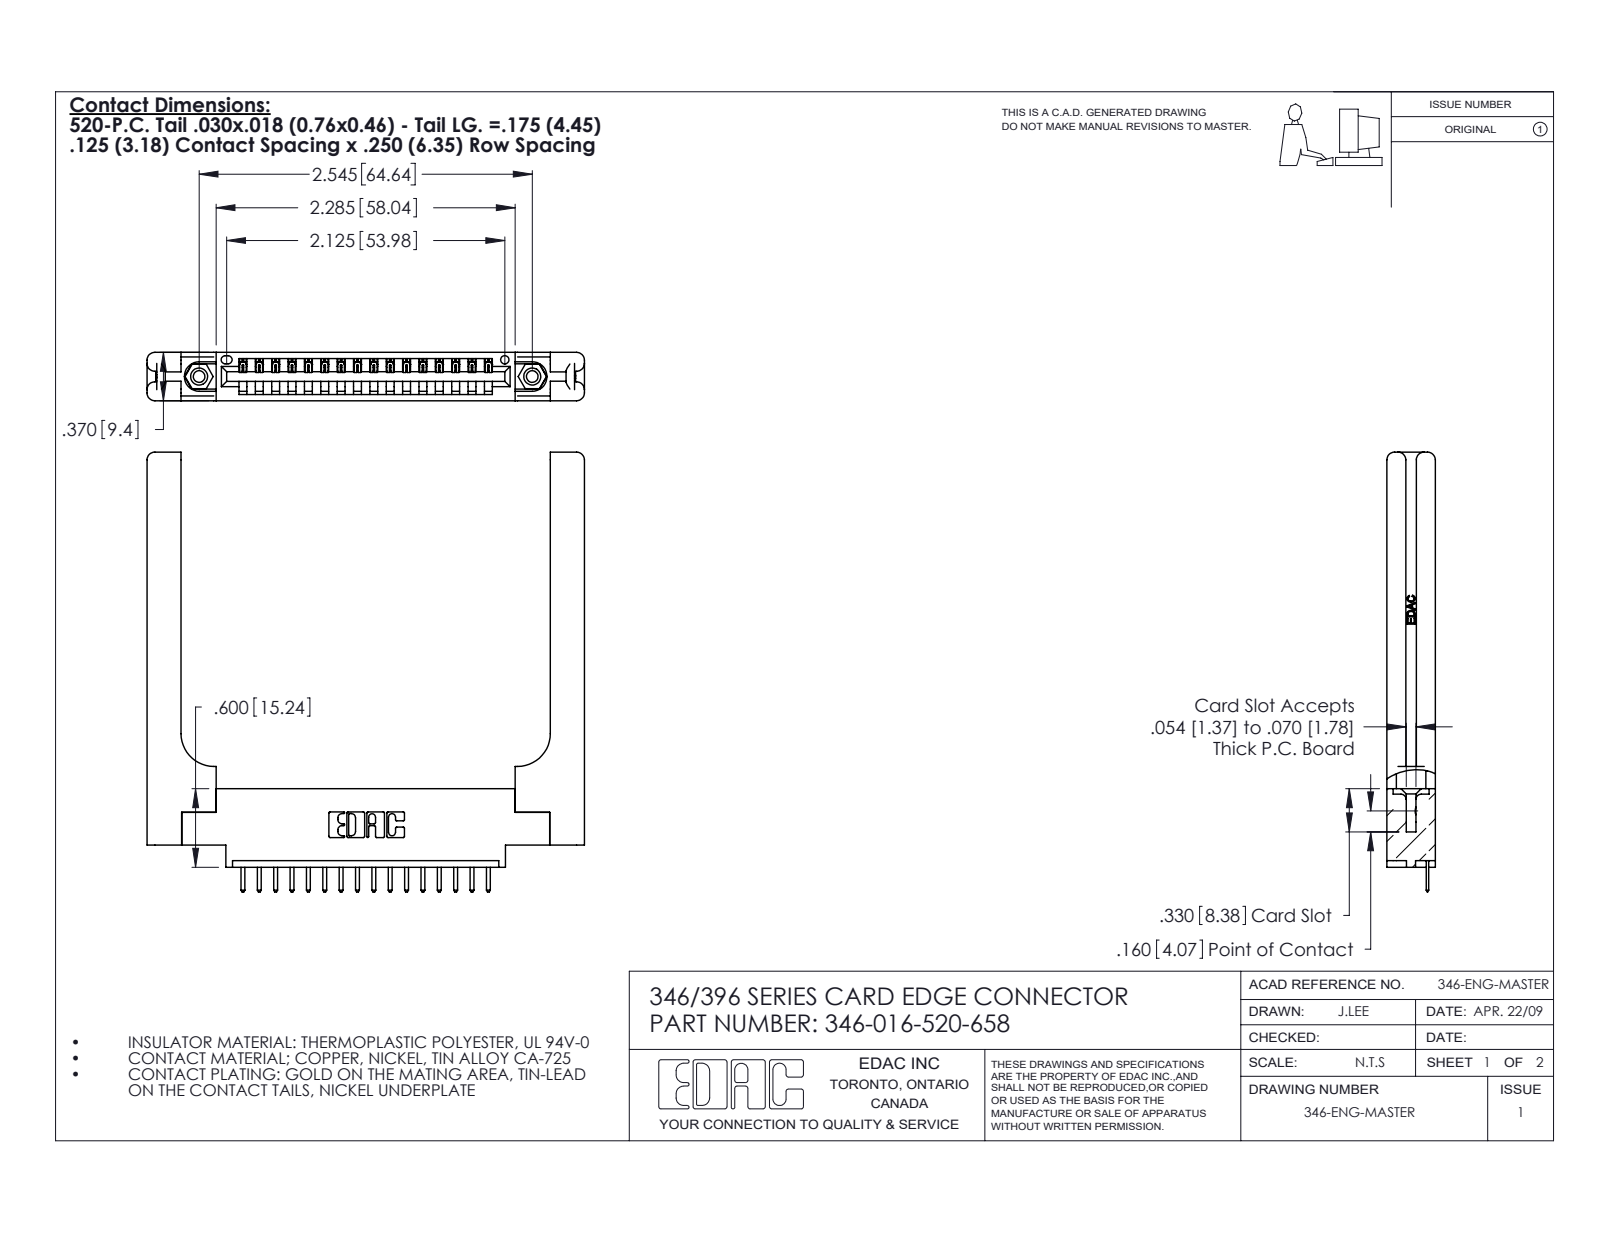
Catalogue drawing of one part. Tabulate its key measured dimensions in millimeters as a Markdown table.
| quantity | value |
| --- | --- |
| part name | 345-292-001_345-293-120; 346-220-058_345-220-058; 346-016-520-658; 345-250-001_345-250-001-102 (+1 more) |
| STEP written by | SolidWorks 2020 (CONFIG_CONTROL_DESIGN) |
| units | millimeters |
| bodies | 21 solids, 1388 faces (914 planar, 414 cylindrical, 60 other) |
| overall size | 85.3 × 84.9 × 9.4 |
| volume | 15 200 mm³ |
| surface area | 14 580 mm² |
| round holes (diameter × count) | 2.3 × 2, 3.2 × 2, 4 × 2, 1.6 × 1 |
| round bosses / shafts (diameter × count) | 3.9 × 2 |
| partial cylindrical surfaces (radius × count) | 0.3 × 34, 0.2 × 32, 0.3 × 22, 1.5 × 16, 0.2 × 6, 0.8 × 6, 0.7 × 3, 0.8 × 2 |
| main face-to-face distances | 9.4, 3.8, 1.8, 3.8, 1.2, 8.2, 2.6, 5.6, 4.4, 6.4 |
| hole center spacings | 6.2, 59.4, 64.6 |
